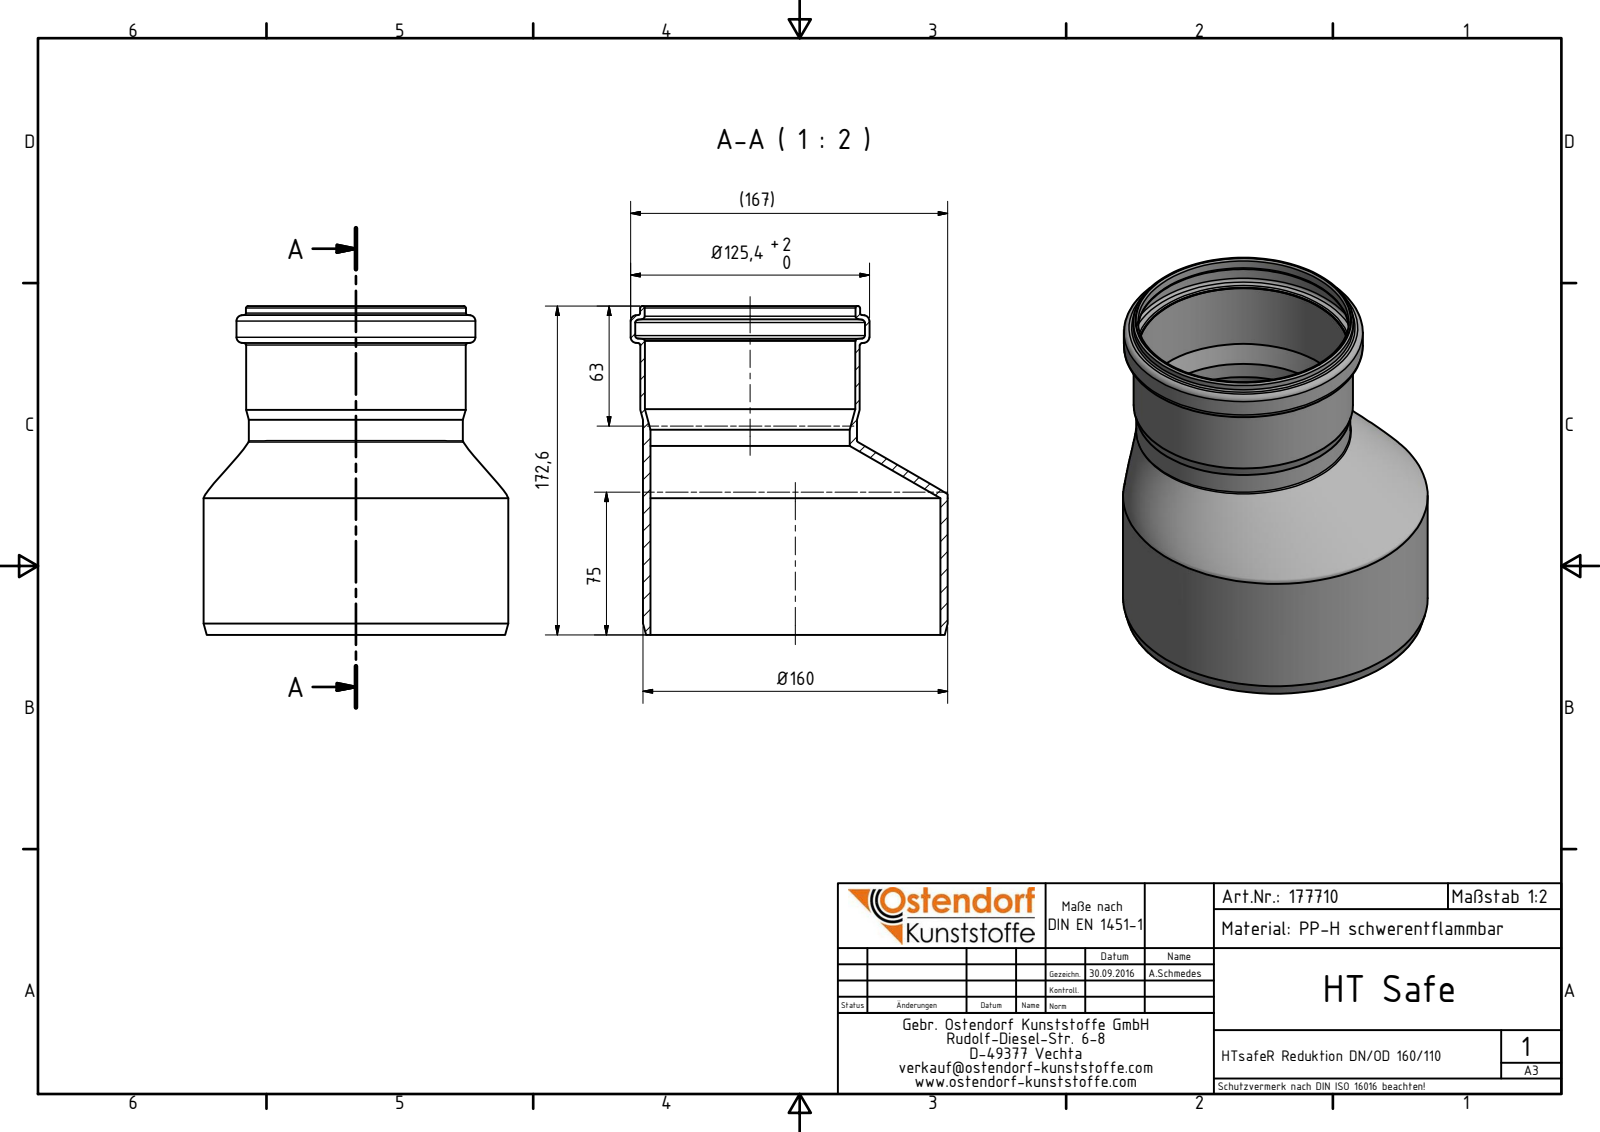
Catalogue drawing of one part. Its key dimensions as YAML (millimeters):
part_name: "177710 HTsafeR DN_OD 160_110"
step_written_by: "Autodesk Inventor 2016 (AUTOMOTIVE_DESIGN)"
units: millimeters
bodies: {solids: 1, faces: 34, planar: 3, cylindrical: 11, other: 20}
overall_size: [172.6, 166.5, 160]
volume: 273263
surface_area: 162077
round_holes:
  - {diameter: 104.6, count: 1}
  - {diameter: 110.4, count: 1}
  - {diameter: 110.7, count: 1}
  - {diameter: 120.6, count: 1}
  - {diameter: 152.2, count: 1}
round_bosses_or_shafts:
  - {diameter: 160, count: 1}
  - {diameter: 125.4, count: 1}
  - {diameter: 115.5, count: 1}
  - {diameter: 115.2, count: 1}
  - {diameter: 112.4, count: 1}
face_to_face_distances: [172.6, 154.29, 18.31]
hole_center_spacings: [23.8]
